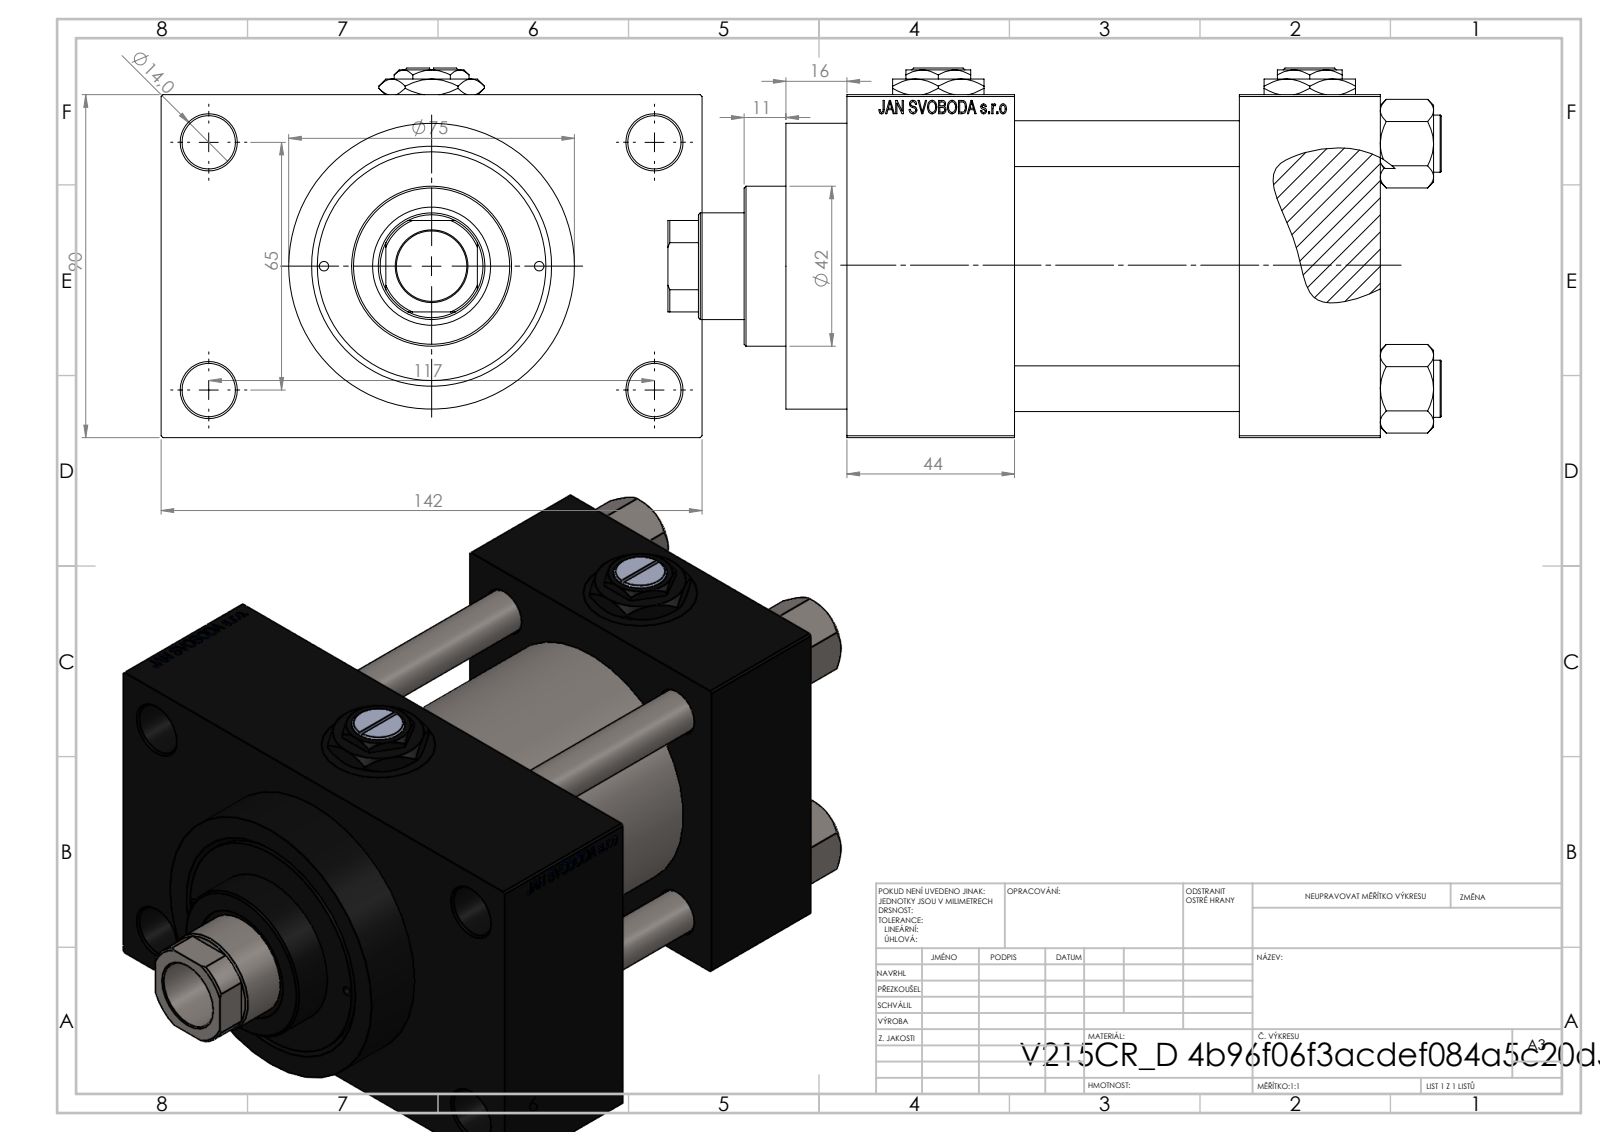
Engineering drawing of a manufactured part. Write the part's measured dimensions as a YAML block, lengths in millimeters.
part_name: "V215_VC_A; NUT_M5_D; V215CR_D_Body; V215CR_D_TYCINKA (+2 more)"
step_written_by: "SolidWorks 2019 (CONFIG_CONTROL_DESIGN)"
units: millimeters
bodies: {solids: 13, faces: 1212, planar: 547, cylindrical: 103, other: 562}
overall_size: [203, 142, 97]
volume: 1090000
surface_area: 204858
round_holes:
  - {diameter: 12, count: 4}
  - {diameter: 14, count: 4}
  - {diameter: 20.96, count: 4}
  - {diameter: 30, count: 4}
  - {diameter: 7, count: 3}
  - {diameter: 2.5, count: 2}
  - {diameter: 18.5, count: 1}
  - {diameter: 28, count: 1}
  - {diameter: 31, count: 1}
  - {diameter: 50, count: 1}
  - {diameter: 60, count: 1}
  - {diameter: 63, count: 1}
round_bosses_or_shafts:
  - {diameter: 15, count: 4}
  - {diameter: 75, count: 1}
  - {diameter: 69, count: 1}
  - {diameter: 42, count: 1}
partial_cylinders:
  - {radius: 13.5, count: 1}
face_to_face_distances: [90, 59, 37, 96, 140, 103, 44, 26, 116, 142]
hole_center_spacings: [26.35, 32.39, 44.4, 45.47, 64.3, 66.92, 68.42, 69.81]
